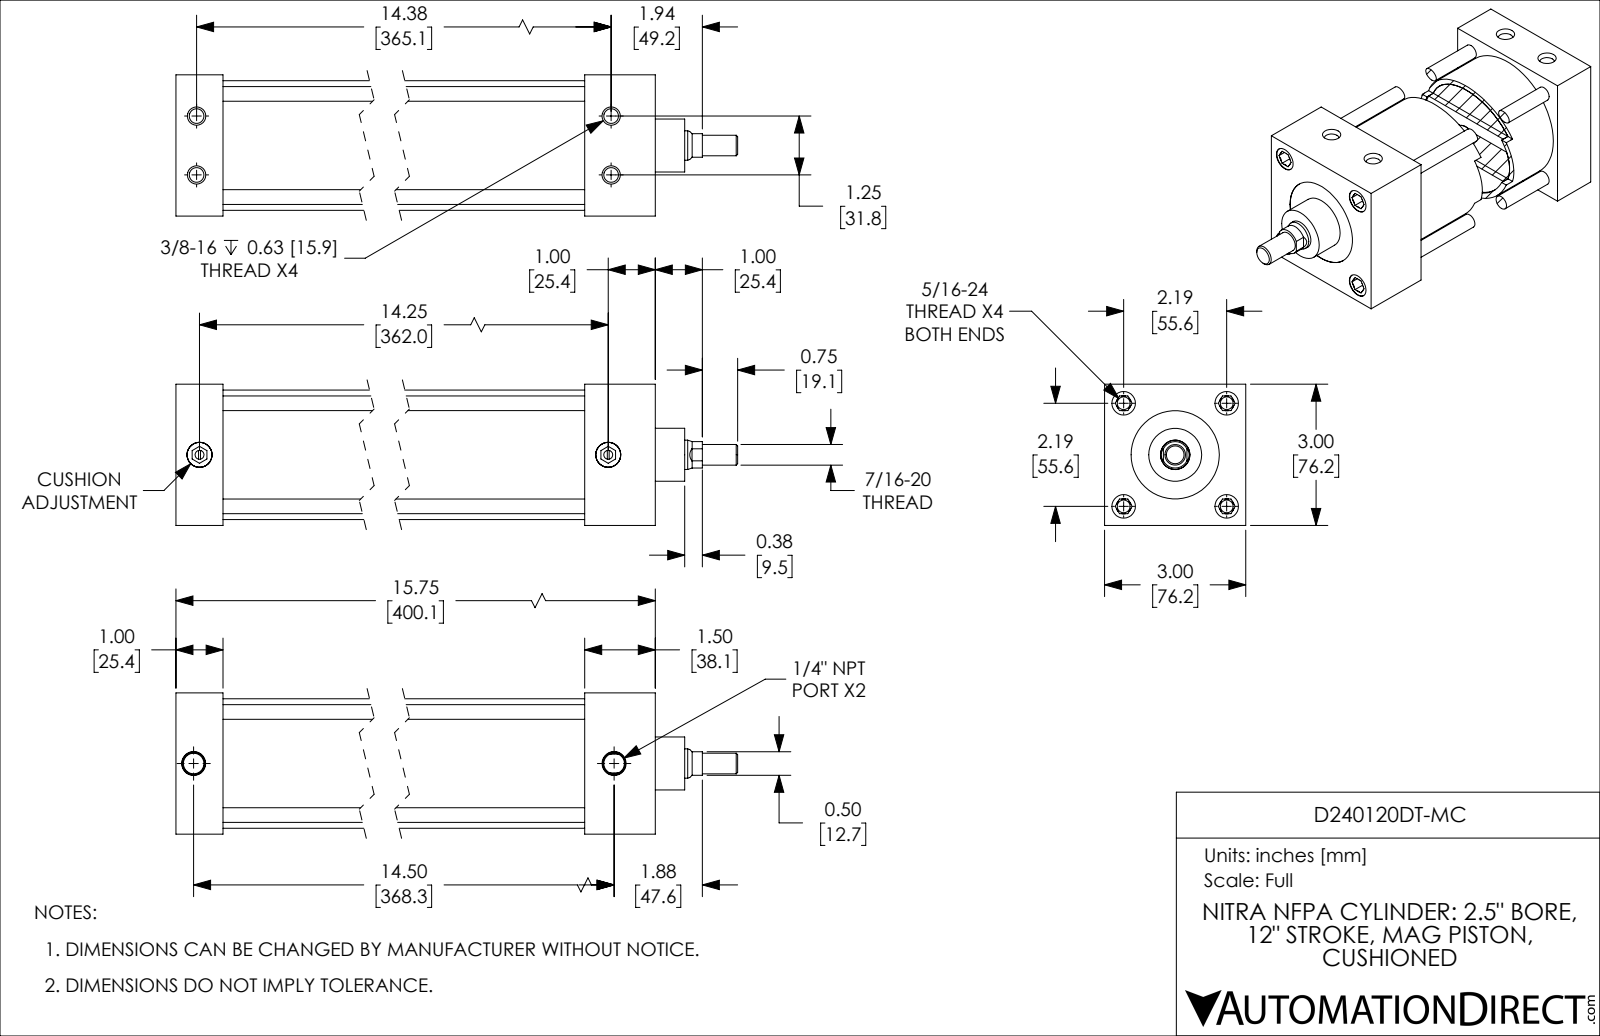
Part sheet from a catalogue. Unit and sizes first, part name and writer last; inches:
Units: inches
Overall size (bounding box): 17.5 × 3 × 3
Round holes (diameter × count): ⌀0.272 ×4, ⌀0.313 ×4, ⌀0.5 ×4, ⌀0.19 ×2, ⌀0.438 ×2, ⌀0.531 ×2, ⌀0.626 ×1, ⌀1.875 ×1, ⌀2.501 ×1
Round bosses / shafts (diameter × count): ⌀0.312 ×4, ⌀0.532 ×2, ⌀2.751 ×1, ⌀2.499 ×1, ⌀1.125 ×1, ⌀0.624 ×1, ⌀0.437 ×1
Partial cylindrical surfaces — rounded edges, fillets, slot ends (radius × count): R0.281 ×1
Main face-to-face distances: 3, 1, 14.25, 13.25, 15.75, 14.75, 1.5, 1.25, 2.25, 12
Hole centre spacings: 1.548, 2.19, 14.451, 0.628, 0.628, 1.25, 3.097, 14.375
Volume: 49.72 in³ · Surface area: 402.8 in²
Bodies: 4 solids, 248 faces (90 planar, 78 cylindrical, 80 other)
Part name (STEP PRODUCT): D240120DT-MC_BODY; D240120DT-MC; D240120DT-MC_PISTON_KK1; D240120DT-MC_CUSHION
STEP written by: SolidWorks 2019 (CONFIG_CONTROL_DESIGN)
